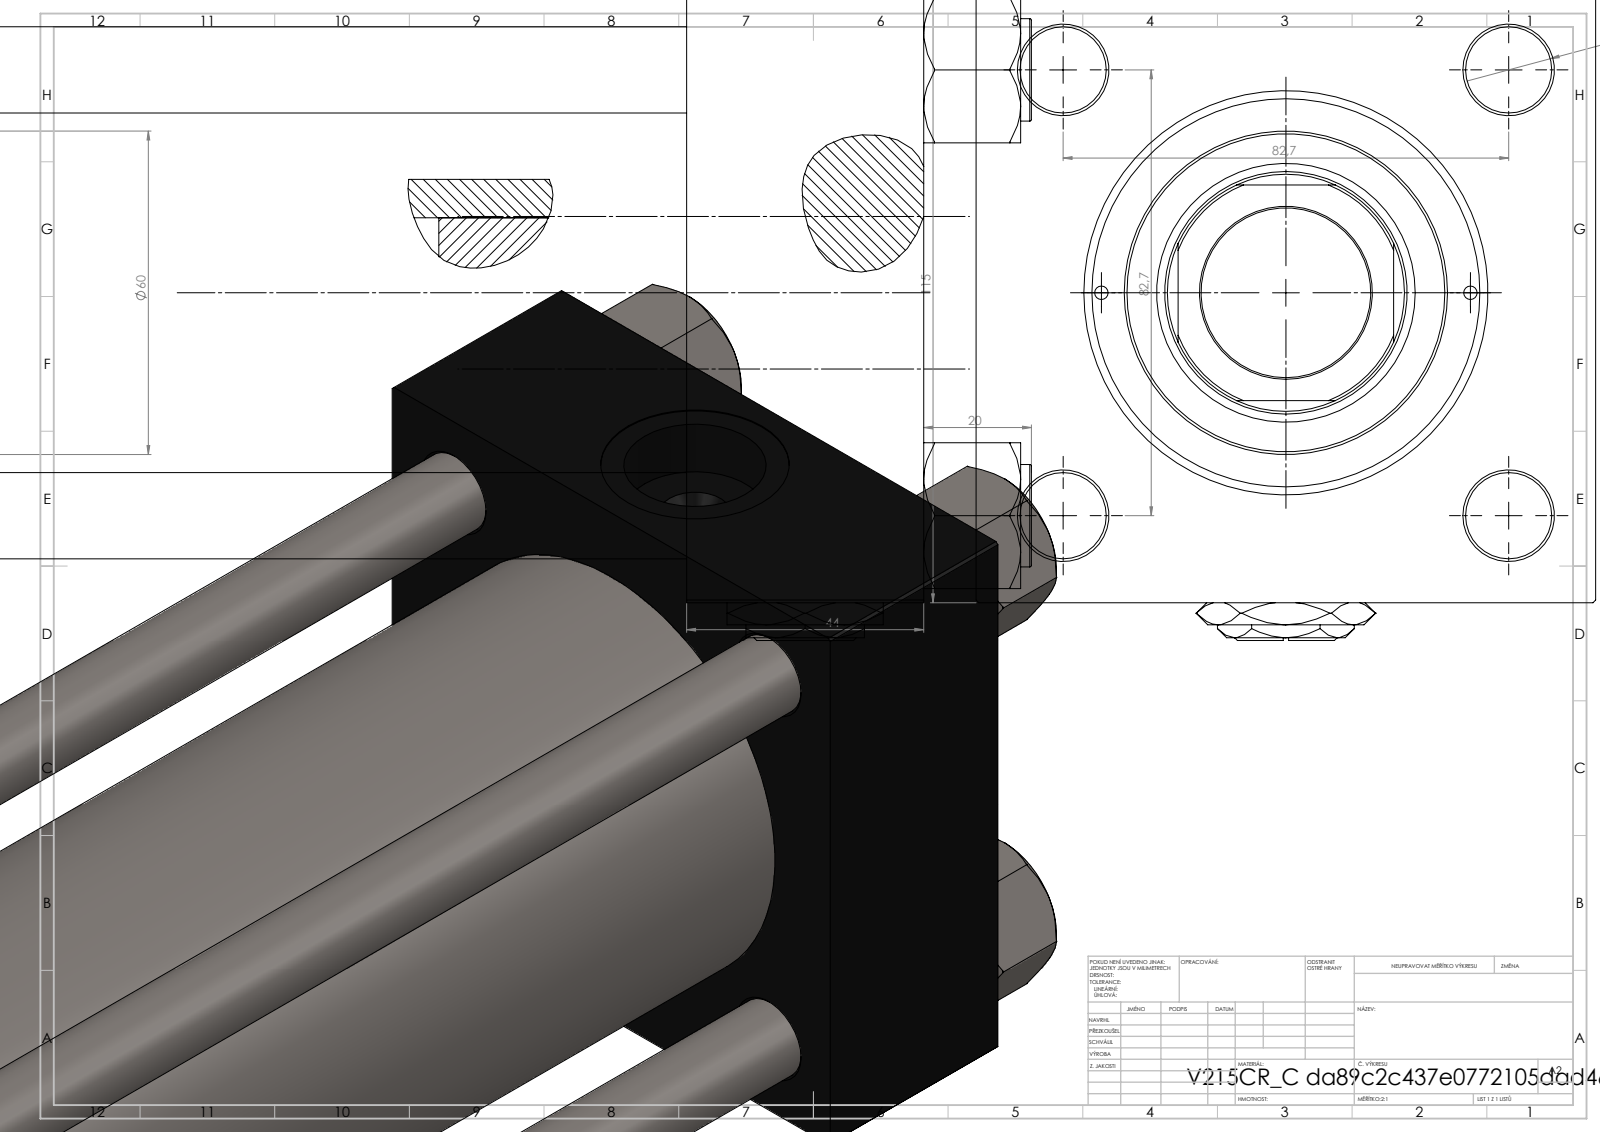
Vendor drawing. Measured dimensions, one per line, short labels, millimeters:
name: V215CR_C_Body; NUT_M5_C; V215CR_VCP_C; Zatka_pro_OIL_PORT (+2 more)
written by: SolidWorks 2019 (CONFIG_CONTROL_DESIGN)
unit: mm
bodies: 13 solids, 1303 faces (623 planar, 102 cylindrical, 578 other)
size: 410 × 122 × 115
volume: 2 376 000 mm³; area: 436 533 mm²
holes: 4× ⌀16, 2× ⌀2.5, 2× ⌀7, 2× ⌀26.44, 2× ⌀35, 1× ⌀31.5, 1× ⌀45, 1× ⌀48, 1× ⌀61, 1× ⌀72, 1× ⌀80
bosses: 4× ⌀19, 1× ⌀86, 1× ⌀60
rounds: 1× R22
face distances: 115, 44, 359, 315, 69, 290, 246, 330.3, 286.3, 40.3
hole spacings: 41.96, 58.48, 82.7, 86.17, 34.25, 116.96, 68.5, 291
